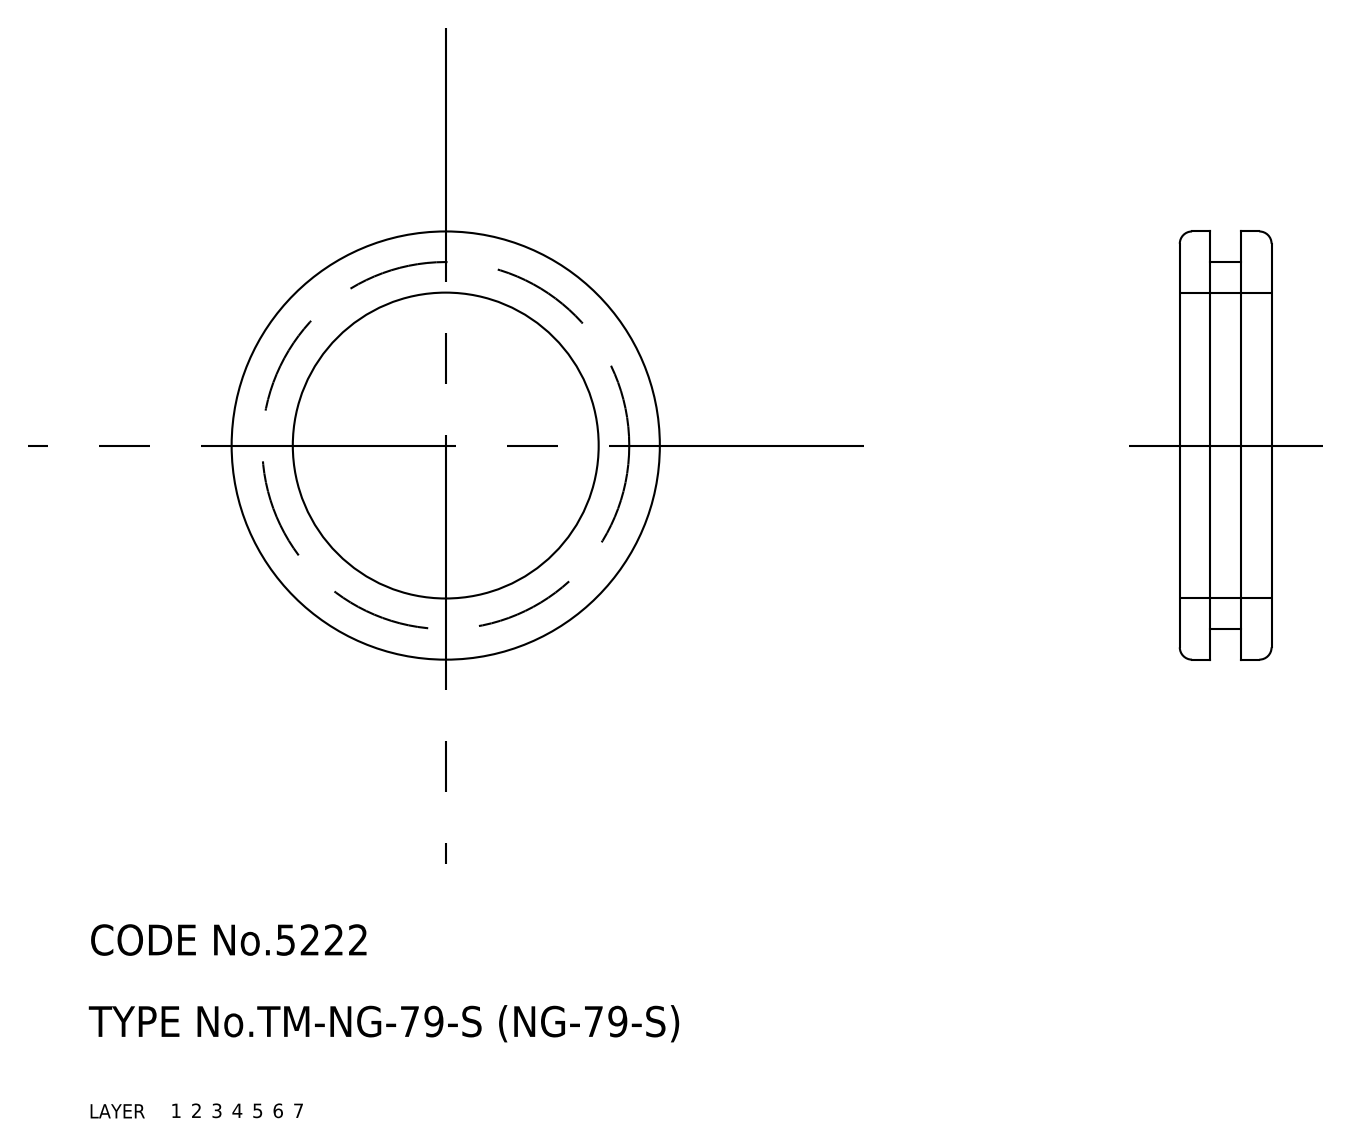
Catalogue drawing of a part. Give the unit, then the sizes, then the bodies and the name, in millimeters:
Units: millimetres
Overall size (bounding box): 42 × 42 × 9
Volume: 4 944 mm³ · Surface area: 3 936 mm²
Bodies: 1 solid, 16 faces (0 planar, 0 cylindrical, 16 other)
Part name (STEP PRODUCT): grommet
STEP written by: CADfix (AUTOMOTIVE_DESIGN)
